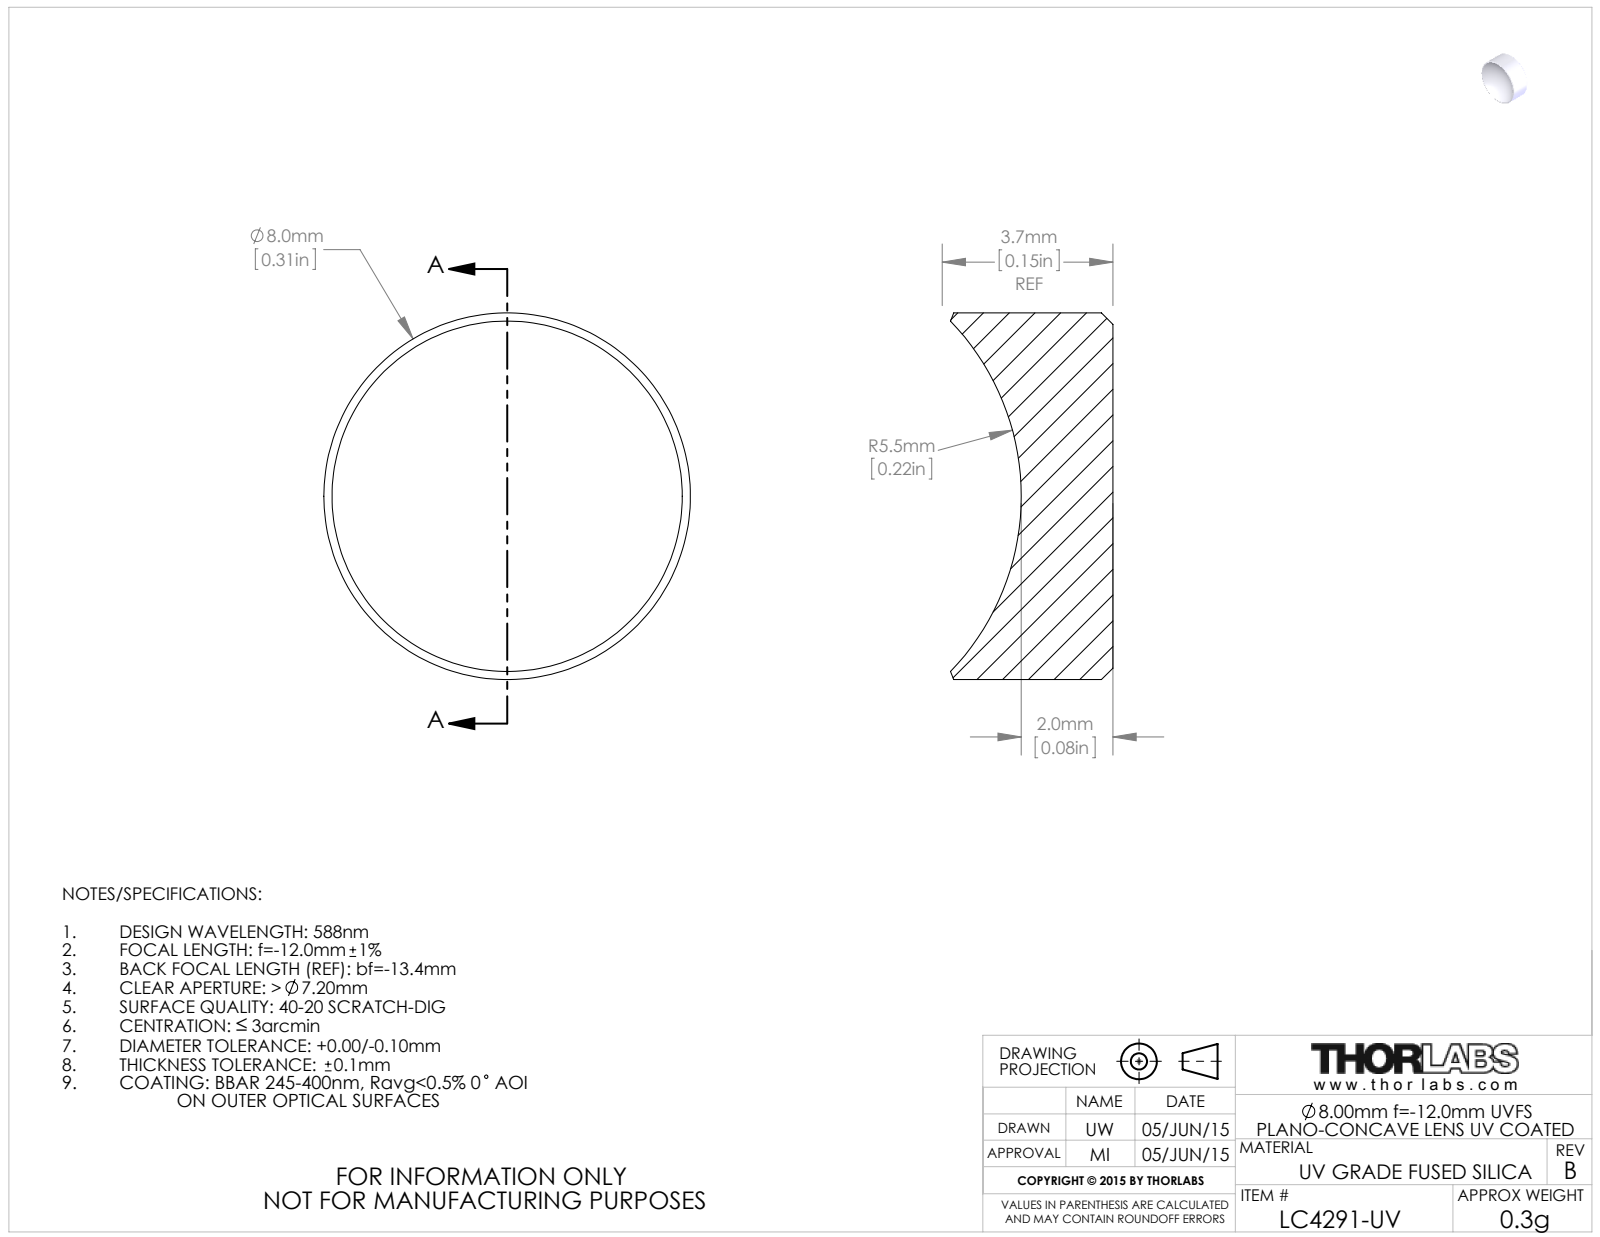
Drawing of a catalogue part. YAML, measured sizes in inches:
part_name: "4342-E0W"
step_written_by: "SolidWorks 2014 (CONFIG_CONTROL_DESIGN)"
units: inches
bodies: {solids: 1, faces: 9, planar: 1, cylindrical: 2, other: 6}
overall_size: [0.315, 0.315, 0.14]
volume: 0.009
surface_area: 0.298
round_bosses_or_shafts:
  - {diameter: 0.315, count: 1}
